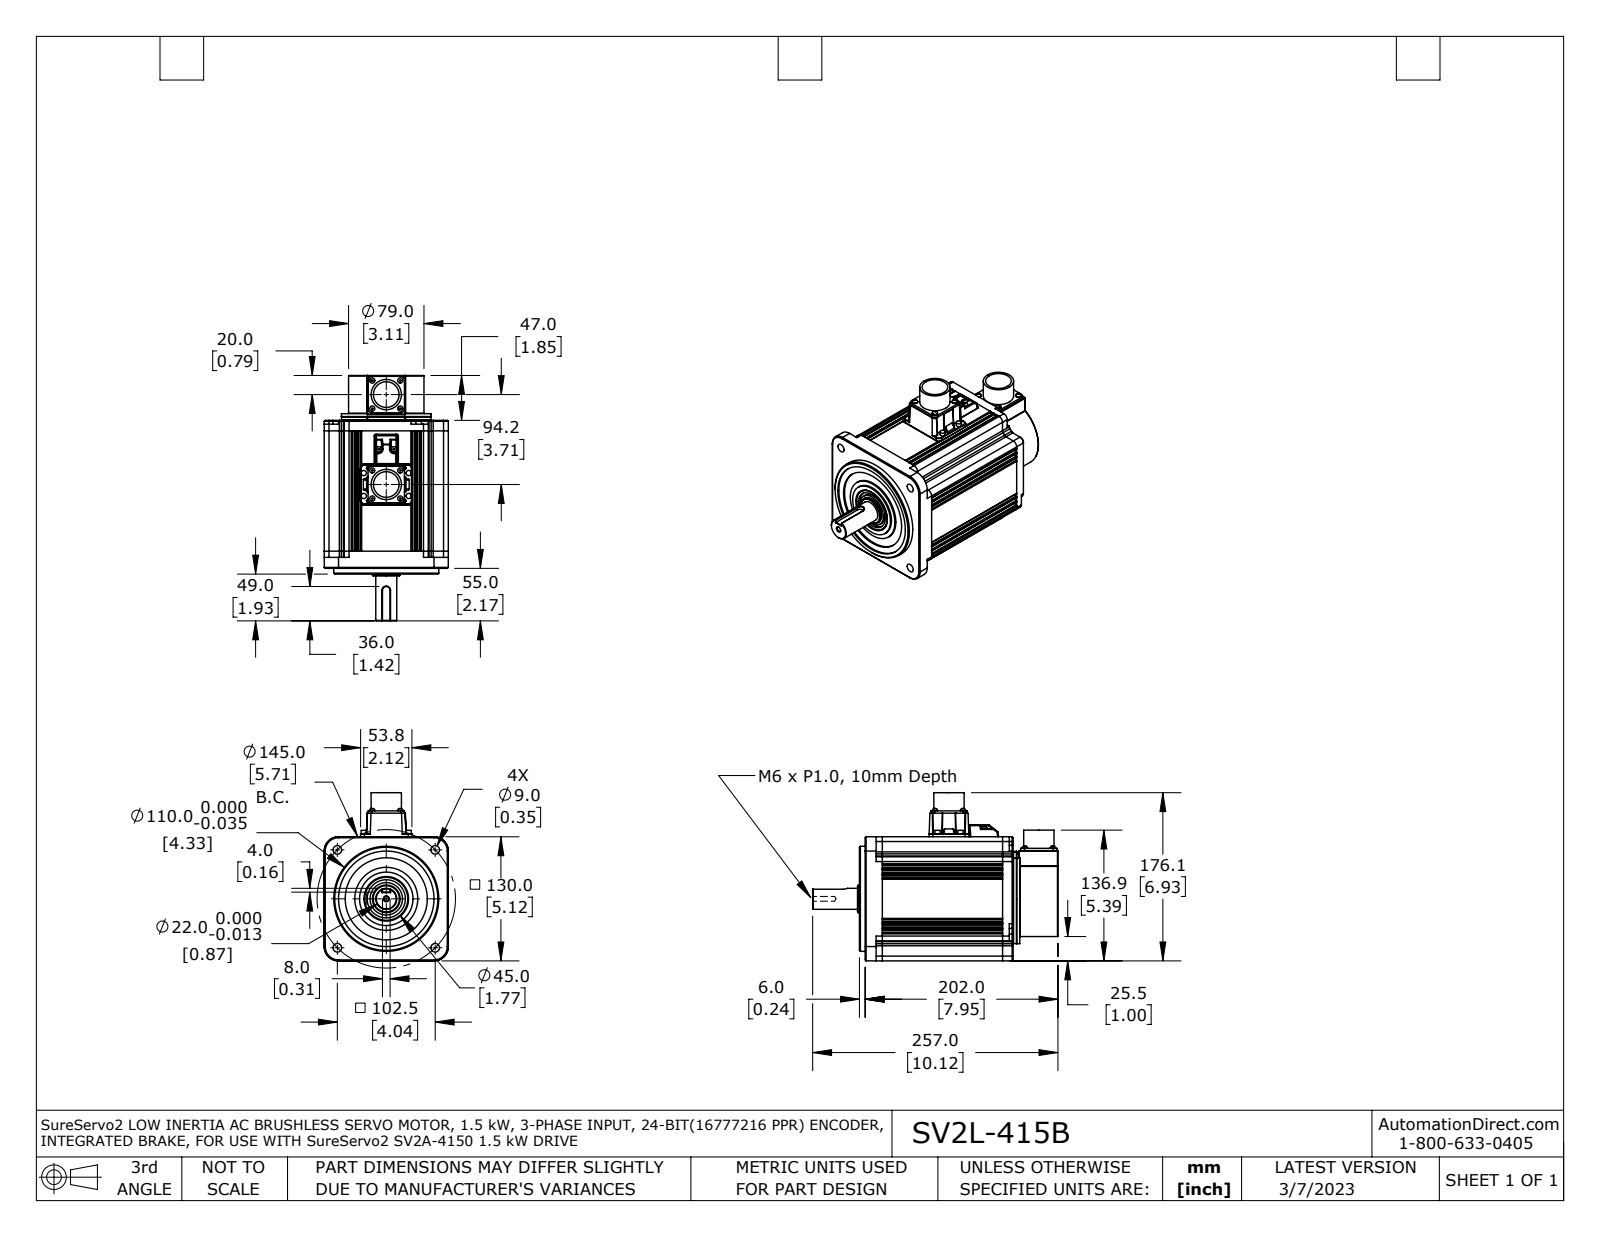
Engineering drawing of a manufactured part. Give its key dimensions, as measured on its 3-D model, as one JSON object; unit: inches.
{"part_name": "SV2M-x15B fxt", "step_written_by": "SolidWorks 2021 (AUTOMOTIVE_DESIGN)", "units": "inches", "bodies": {"solids": 2, "faces": 732, "planar": 310, "cylindrical": 246, "other": 176}, "overall_size": [10.118, 6.935, 5.118], "volume_in3": 165.5, "surface_area_in2": 262.9, "round_holes": [[0.354, 4], [1.058, 2], [0.197, 1], [1.142, 1], [1.575, 1], [1.772, 1], [3.386, 1], [3.937, 1]], "round_bosses_or_shafts": [[0.217, 8], [0.213, 6], [1.25, 2], [4.331, 1], [3.701, 1], [3.11, 1], [2.598, 1], [2.205, 1]], "partial_cylinders_radius": [[0.039, 87], [0.02, 34], [0.157, 17], [0.118, 8], [0.197, 8], [0.079, 2]], "face_to_face_distances": [0.827, 4.291, 5.118, 2.402, 0.211, 0.959, 6.102, 1.85, 3.465, 7.953], "hole_center_spacings": [2.855, 4.037, 5.709, 3.708]}
